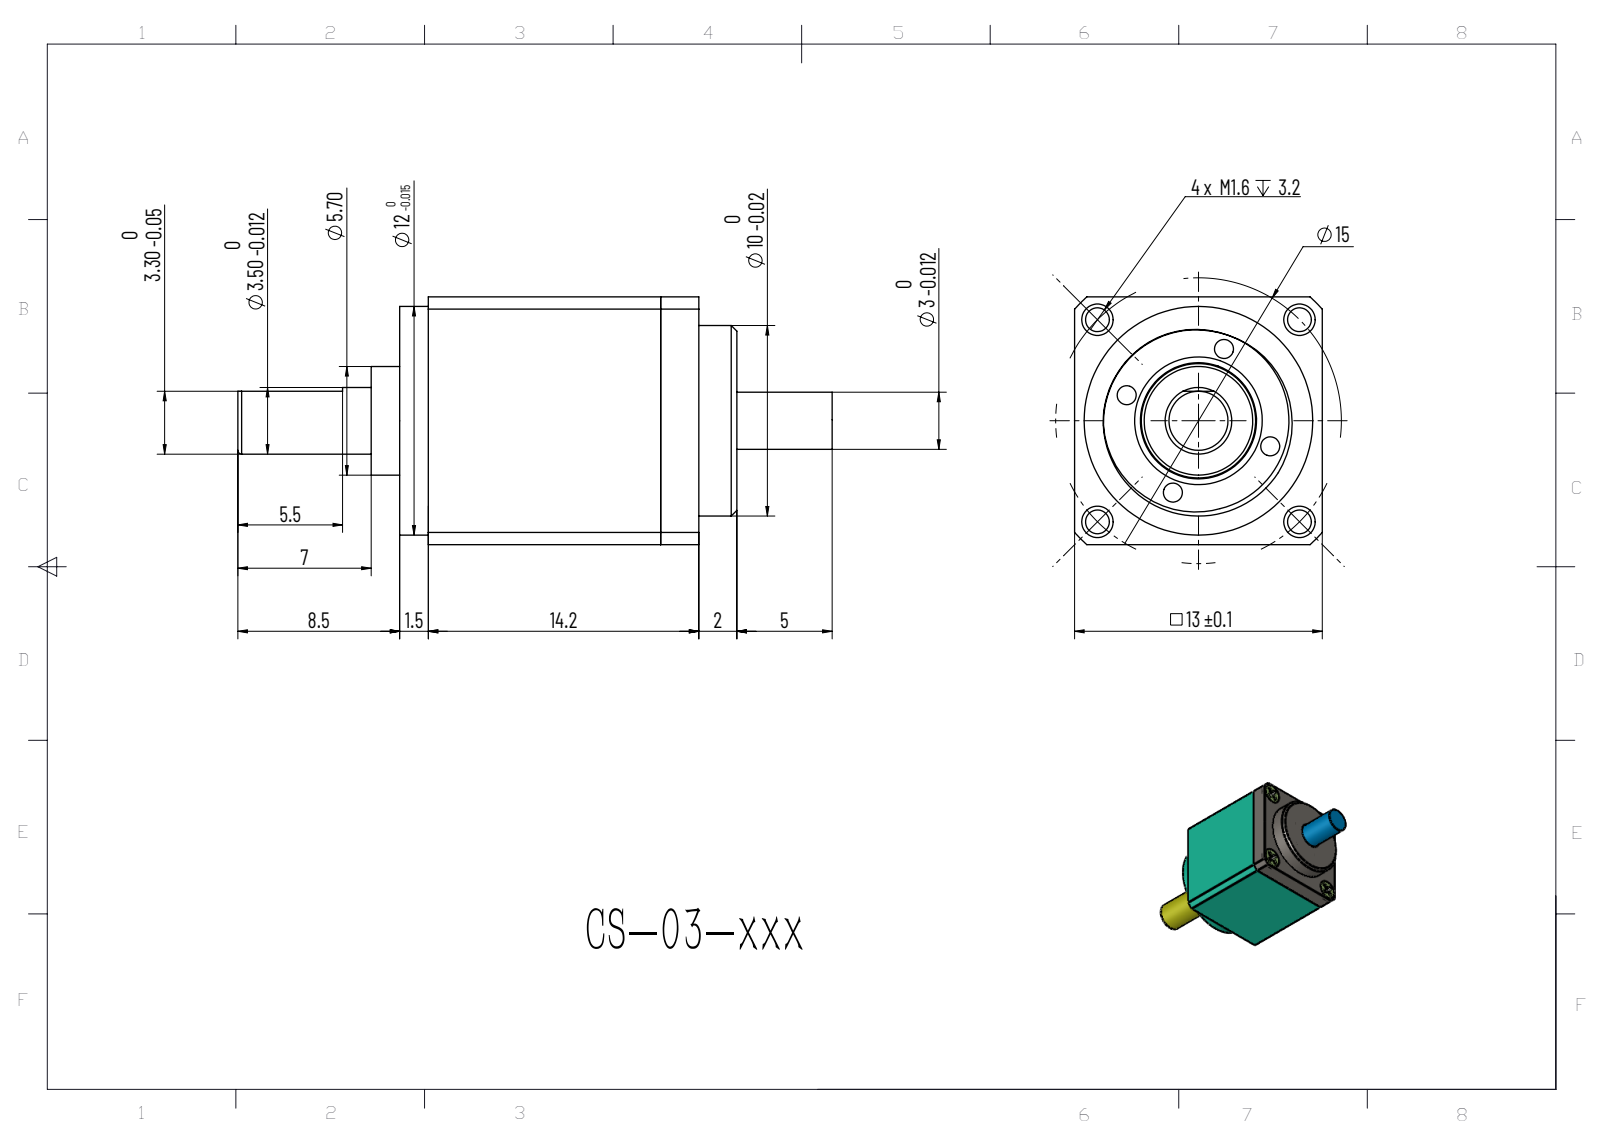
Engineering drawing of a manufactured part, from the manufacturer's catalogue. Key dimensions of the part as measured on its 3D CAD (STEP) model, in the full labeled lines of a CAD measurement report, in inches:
Part name (STEP PRODUCT): HS-CS-03-1U; ??675Z 8x5x2.5_??; CS-03-1U-02_??; CS-03-1U-04_?? (+8 more)
STEP written by: ONSHAPE BY PTC INC, 1.201 (AP242_MANAGED_MODEL_BASED_3D_ENGINEERING_MIM_LF)
Units: inches
Bodies: 30 solids, 1263 faces (191 planar, 849 cylindrical, 223 other)
Overall size (bounding box): 1.24 × 0.528 × 0.528
Volume: 0.15 in³ · Surface area: 6.95 in²
Round holes (diameter × count): ⌀0.049 ×6, ⌀0.039 ×4, ⌀0.071 ×4, ⌀0.063 ×1, ⌀0.079 ×1, ⌀0.118 ×1, ⌀0.138 ×1, ⌀0.157 ×1, ⌀0.177 ×1, ⌀0.189 ×1, ⌀0.197 ×1, ⌀0.223 ×1
Round bosses / shafts (diameter × count): ⌀0.11 ×4, ⌀0.063 ×4, ⌀0.055 ×4, ⌀0.472 ×1, ⌀0.394 ×1, ⌀0.326 ×1, ⌀0.315 ×1, ⌀0.268 ×1
Partial cylindrical surfaces — rounded edges, fillets, slot ends (radius × count): R0.069 ×100, R0.069 ×100, R0.07 ×100, R0.074 ×100, R0.075 ×100, R0.198 ×100, R0.171 ×1, R0.344 ×1
Main face-to-face distances: 0.512, 0.079, 0.098, 0.059, 0.539, 0.618, 0.02, 0.598, 0.138, 0.108
Hole centre spacings: 0.418, 0.178, 0.295, 0.142, 0.428, 0.591, 0.2, 0.267
